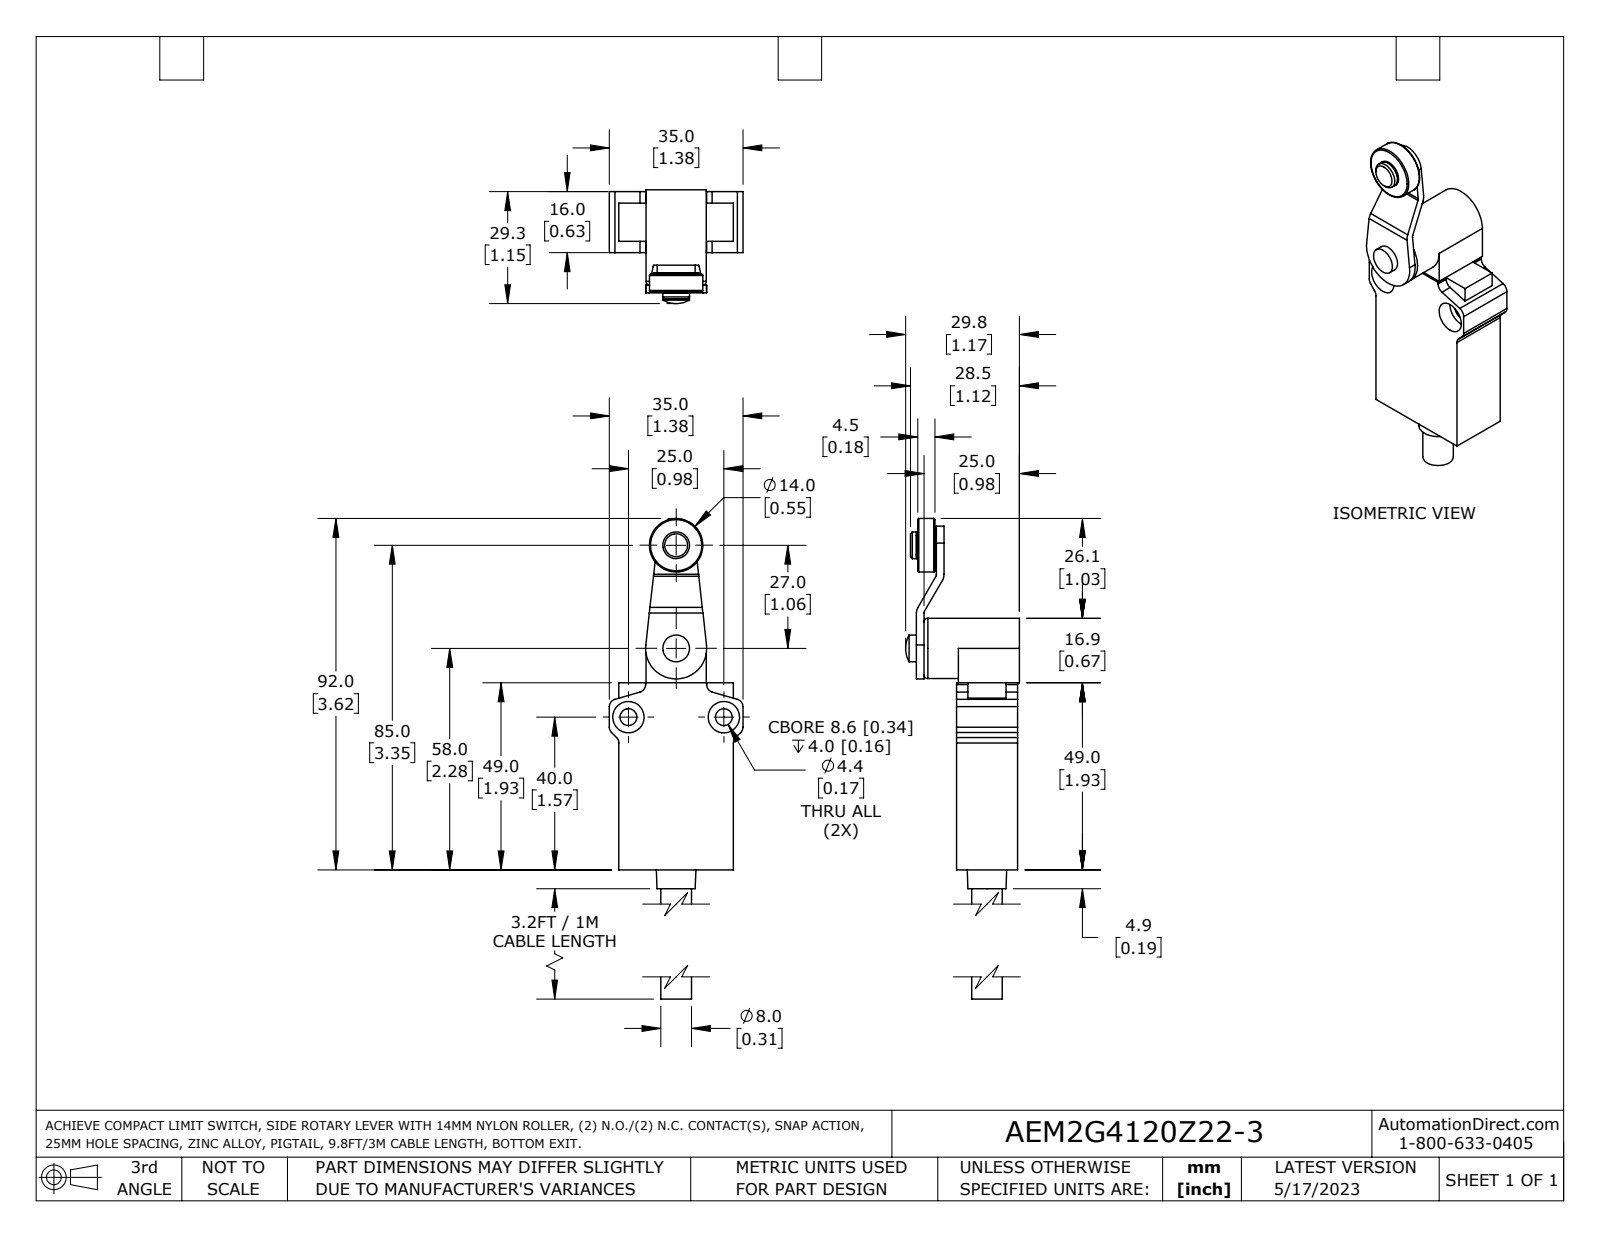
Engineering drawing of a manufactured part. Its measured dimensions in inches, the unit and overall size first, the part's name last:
Units: inches
Overall size (bounding box): 4.209 × 1.378 × 1.174
Round holes (diameter × count): ⌀0.173 ×2, ⌀0.323 ×2, ⌀0.197 ×1
Round bosses / shafts (diameter × count): ⌀0.276 ×2, ⌀0.622 ×1, ⌀0.551 ×1, ⌀0.315 ×1, ⌀0.197 ×1
Partial cylindrical surfaces — rounded edges, fillets, slot ends (radius × count): R0.079 ×8, R0.039 ×2, R0.118 ×2, R0.197 ×1, R0.256 ×1, R0.315 ×1
Main face-to-face distances: 0.63, 1.181, 0.079, 0.207, 0.02, 0.28, 0.902, 1.929, 0.65, 0.128
Hole centre spacings: 0.863, 0.984
Volume: 1.862 in³ · Surface area: 15.59 in²
Bodies: 1 solid, 97 faces (55 planar, 36 cylindrical, 6 other)
Part name (STEP PRODUCT): AEM2G4120Z22-3
STEP written by: SolidWorks 2021 (AUTOMOTIVE_DESIGN)
